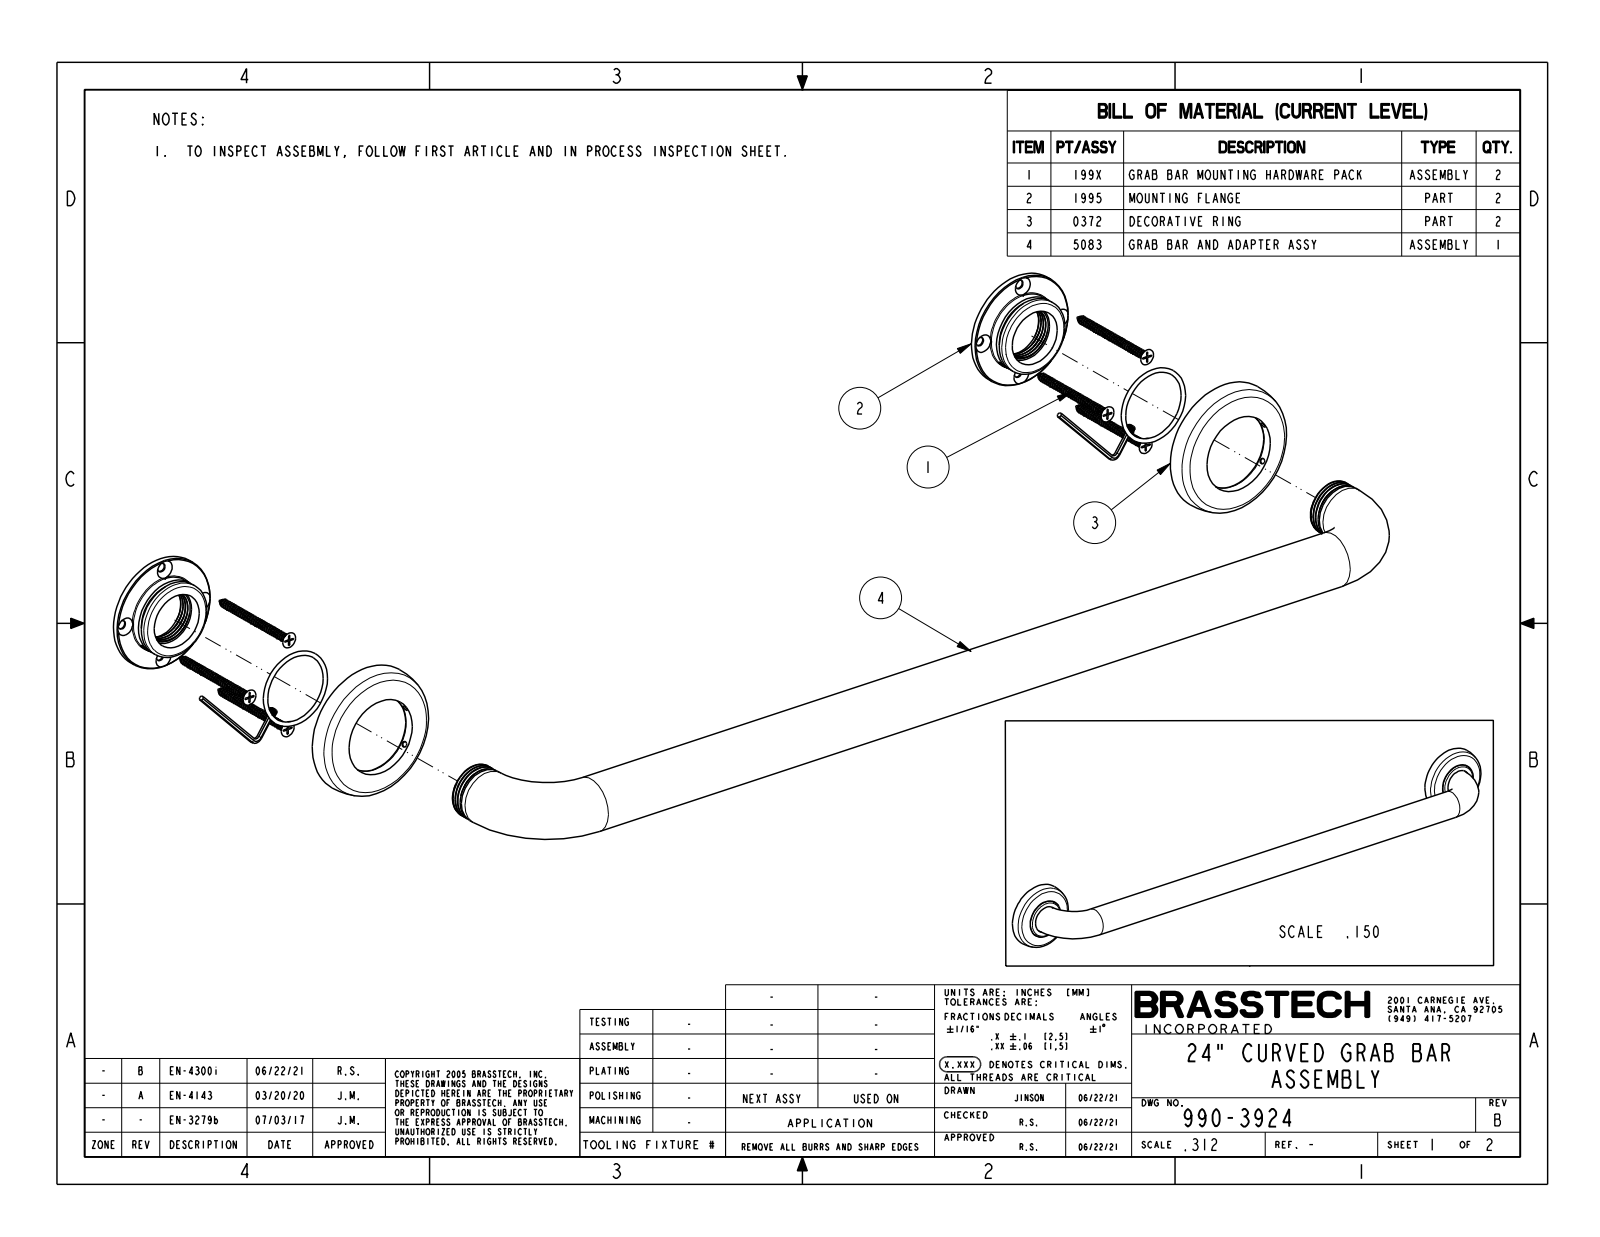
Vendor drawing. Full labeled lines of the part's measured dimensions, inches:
Part name (STEP PRODUCT): 1995; 20-287_ASM; 80529; 50869 (+3 more)
STEP written by: PRO/ENGINEER BY PARAMETRIC TECHNOLOGY CORPORATION, 2013150 (CONFIG_CONTROL_DESIGN)
Units: inches
Bodies: 7 solids, 752 faces (228 planar, 200 cylindrical, 324 other)
Overall size (bounding box): 27 × 3 × 2.912
Volume: 9.024 in³ · Surface area: 416.3 in²
Round holes (diameter × count): ⌀0.202 ×8, ⌀0.1 ×4, ⌀1.152 ×3, ⌀0.163 ×2, ⌀0.866 ×2, ⌀1.16 ×2, ⌀1.26 ×2, ⌀1.77 ×2
Round bosses / shafts (diameter × count): ⌀1.75 ×4, ⌀0.126 ×4, ⌀1.25 ×3, ⌀2.6 ×2, ⌀1.928 ×2, ⌀1.594 ×2, ⌀1.237 ×2, ⌀1.147 ×2
Partial cylindrical surfaces — rounded edges, fillets, slot ends (radius × count): R0.212 ×8, R0.038 ×4, R0.025 ×2
Main face-to-face distances: 0.15, 0.45, 0.6, 0.074, 0.076, 0.526, 0.1, 0.35, 0.25, 0.05
Hole centre spacings: 1.087, 1.538, 24, 2.175, 22.939, 24.025, 25.111, 0.084
